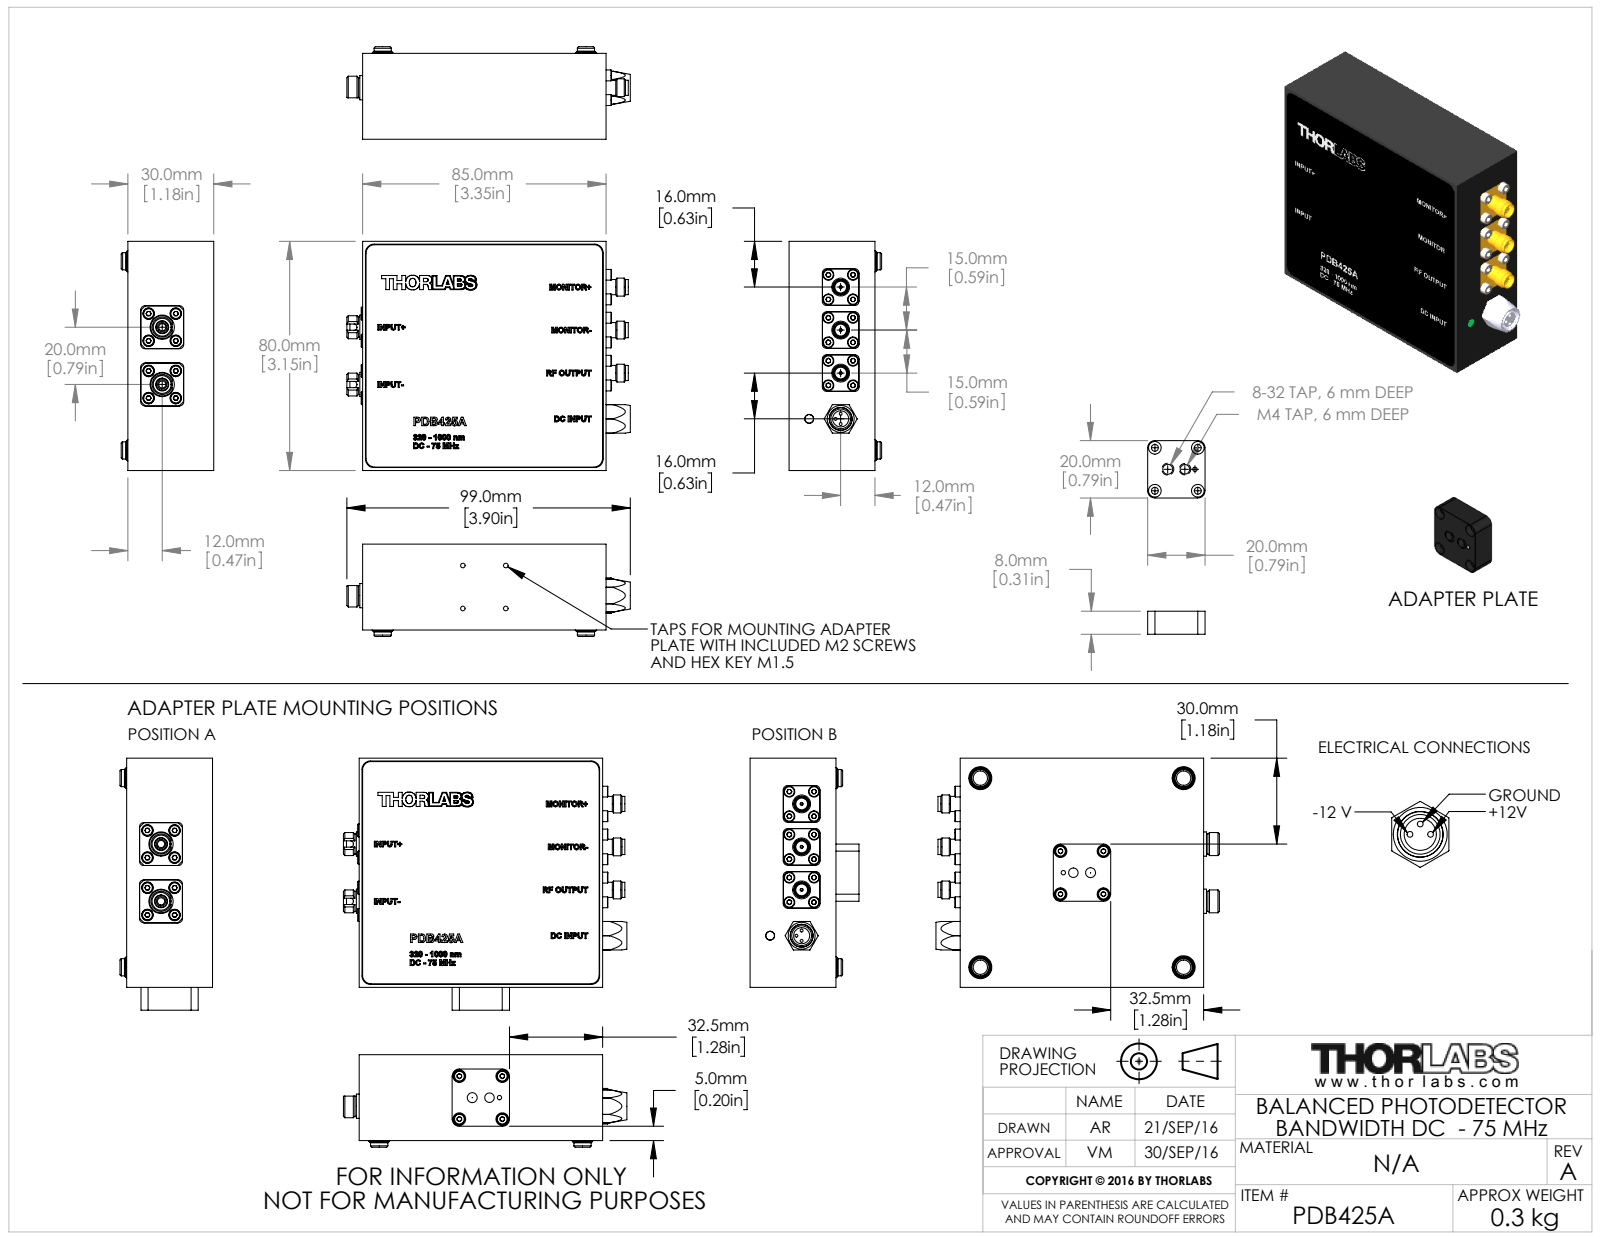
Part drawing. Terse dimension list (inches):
name: MTN005467-E0W
written by: SolidWorks 2014 (AUTOMOTIVE_DESIGN)
unit: in
bodies: 90 solids, 3020 faces (1757 planar, 584 cylindrical, 679 other)
size: 3.898 × 3.465 × 1.496
volume: 5.353 in³; area: 89.6 in²
holes: 38× ⌀0.063, 12× ⌀0.102, 8× ⌀0.087, 8× ⌀0.094, 8× ⌀0.157, 8× ⌀0.173, 6× ⌀0.04, 5× ⌀0.315, 3× ⌀0.031, 3× ⌀0.039, 3× ⌀0.161, 3× ⌀0.165
bosses: 20× ⌀0.15, 20× ⌀0.079, 8× ⌀0.177, 8× ⌀0.098, 6× ⌀0.017, 4× ⌀0.236, 3× ⌀0.245, 3× ⌀0.209
rounds: 20× R0.059, 12× R0.118, 8× R0.098, 8× R0.197, 4× R0.039, 2× R0.374, 1× R0.226
face distances: 1.169, 0.236, 0.933, 0.217, 3.15, 0.079, 2.933, 3.346, 0.138, 3.268
hole spacings: 0.591, 0.239, 0.339, 0.374, 0.265, 0.344, 0.454, 0.508
